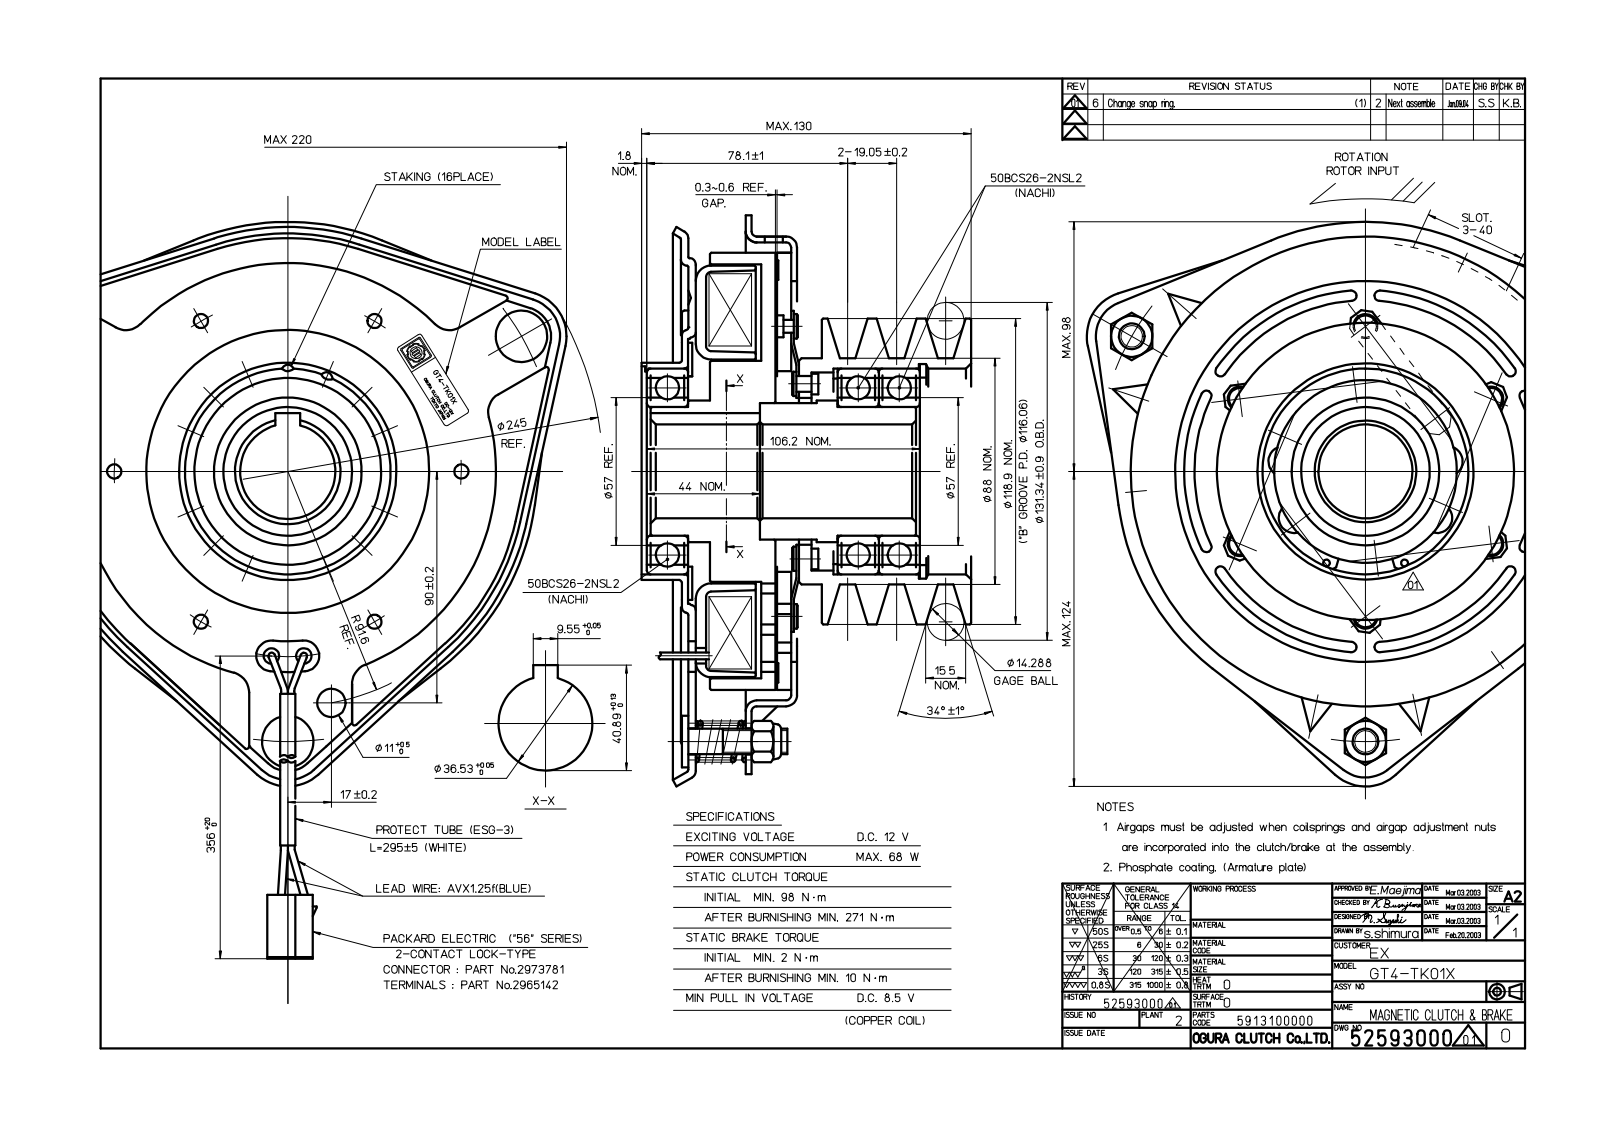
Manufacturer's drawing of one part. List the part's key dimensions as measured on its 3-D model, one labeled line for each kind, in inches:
Part name (STEP PRODUCT): MGCL&BR
STEP written by: SolidWorks 2014 (CONFIG_CONTROL_DESIGN)
Units: inches
Bodies: 1 solid, 1000 faces (369 planar, 366 cylindrical, 265 other)
Overall size (bounding box): 8.598 × 8.451 × 5.043
Volume: 82.63 in³ · Surface area: 428.8 in²
Round holes (diameter × count): ⌀0.201 ×6, ⌀0.24 ×6, ⌀0.433 ×4, ⌀0.402 ×3, ⌀0.465 ×3, ⌀0.087 ×2, ⌀0.106 ×2, ⌀1.438 ×1, ⌀2.244 ×1, ⌀2.835 ×1, ⌀2.858 ×1, ⌀2.913 ×1
Round bosses / shafts (diameter × count): ⌀0.374 ×12, ⌀0.276 ×6, ⌀0.236 ×6, ⌀0.197 ×6, ⌀0.787 ×3, ⌀0.543 ×3, ⌀0.38 ×3, ⌀0.295 ×2
Partial cylindrical surfaces — rounded edges, fillets, slot ends (radius × count): R0.118 ×28, R0.079 ×16, R0.039 ×12, R0.142 ×12, R0.236 ×12, R0.102 ×6, R0.339 ×6, R0.551 ×3
Main face-to-face distances: 0.114, 0.126, 1.575, 1.244, 1.323, 1.654, 0.079, 1.461, 1.539, 0.24
Hole centre spacings: 1.339, 2.22, 1.772, 3.006, 4.941, 0.907, 2.099, 2.319
